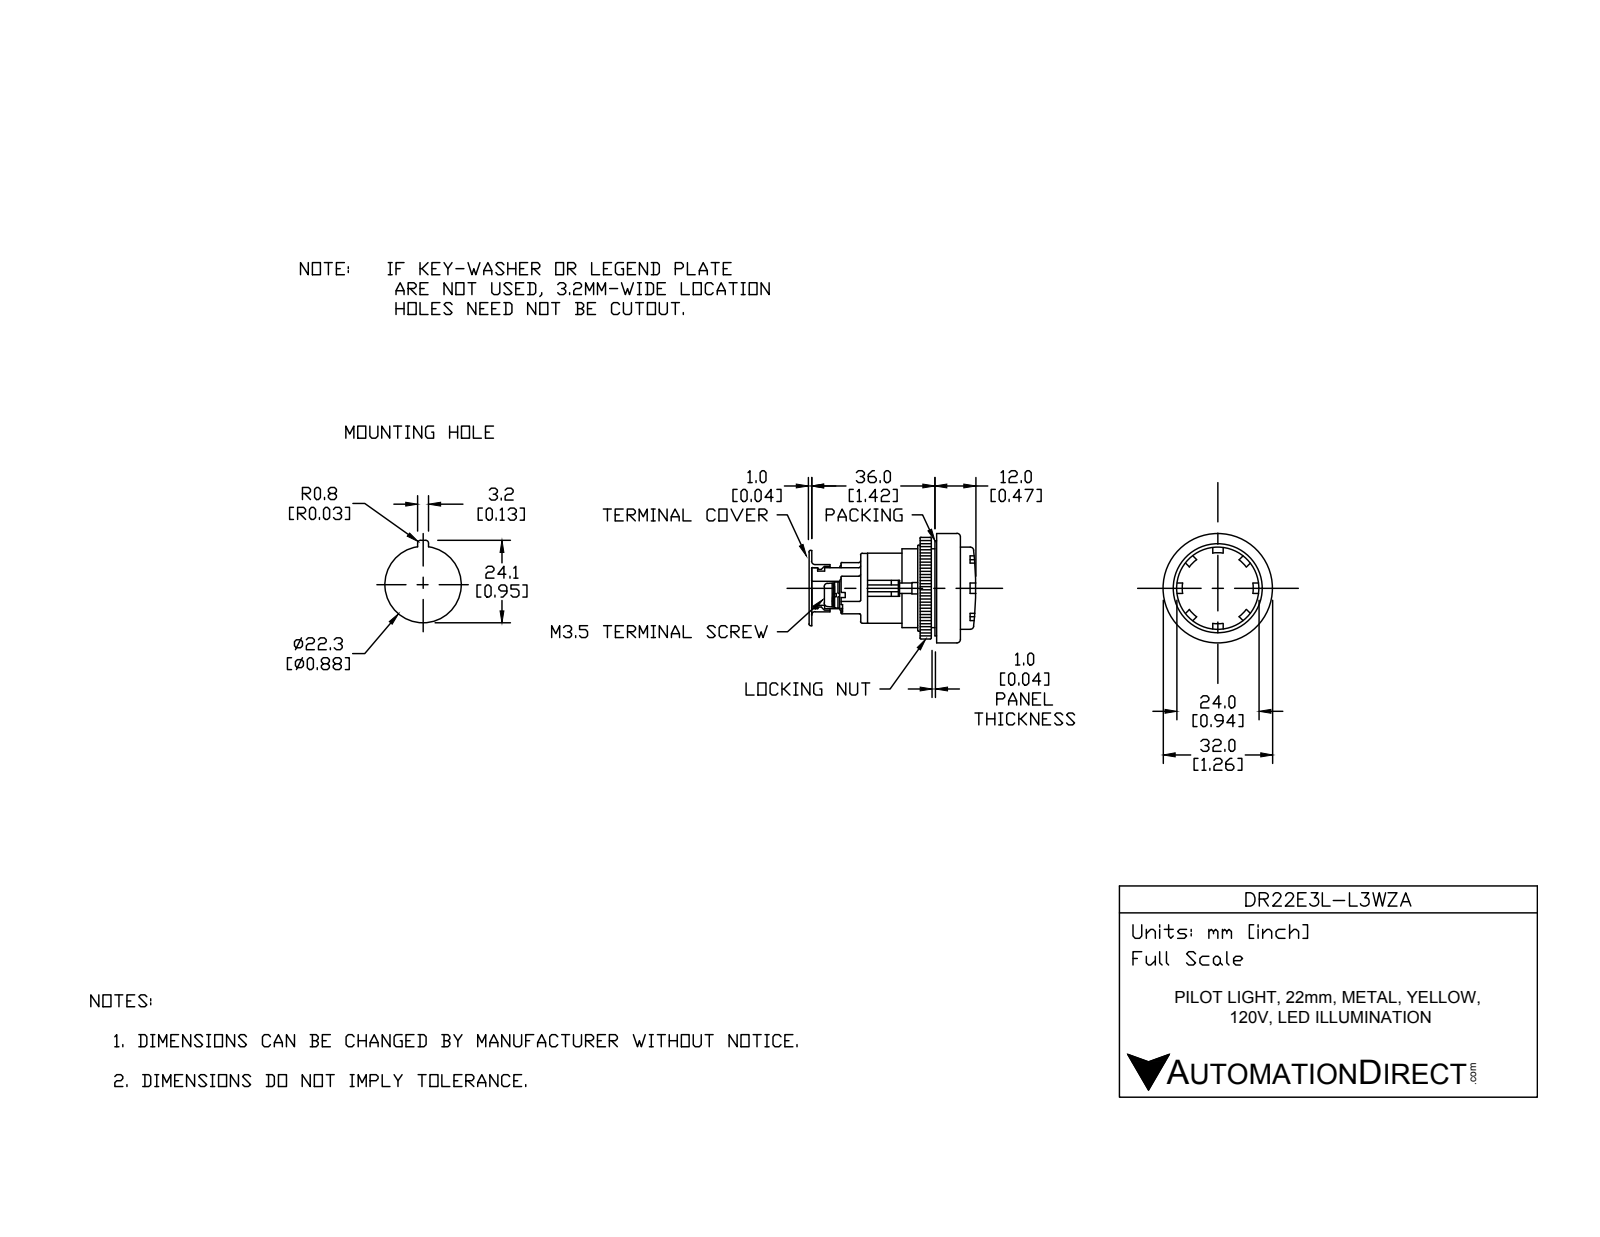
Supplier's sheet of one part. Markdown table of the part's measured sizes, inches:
| quantity | value |
| --- | --- |
| part name | DR22E3L-L3YZA |
| STEP written by | SolidWorks 2017 (AUTOMOTIVE_DESIGN) |
| units | inches |
| bodies | 12 solids, 232 faces (165 planar, 51 cylindrical, 16 other) |
| overall size | 2.913 × 1.26 × 1.26 |
| volume | 2.435 in³ |
| surface area | 28.15 in² |
| round holes (diameter × count) | 0.866 × 1, 0.886 × 1, 0.984 × 1, 1.181 × 1 |
| round bosses / shafts (diameter × count) | 0.217 × 2, 1.26 × 1, 1.169 × 1, 1.161 × 1, 1.063 × 1, 0.858 × 1 |
| partial cylindrical surfaces (radius × count) | 0.02 × 14, 0.128 × 4, 0.039 × 1, 0.197 × 1 |
| main face-to-face distances | 0.748, 1.181, 1.055, 0.039, 0.157, 0.236, 0.819, 0.433, 1.28, 0.063 |
